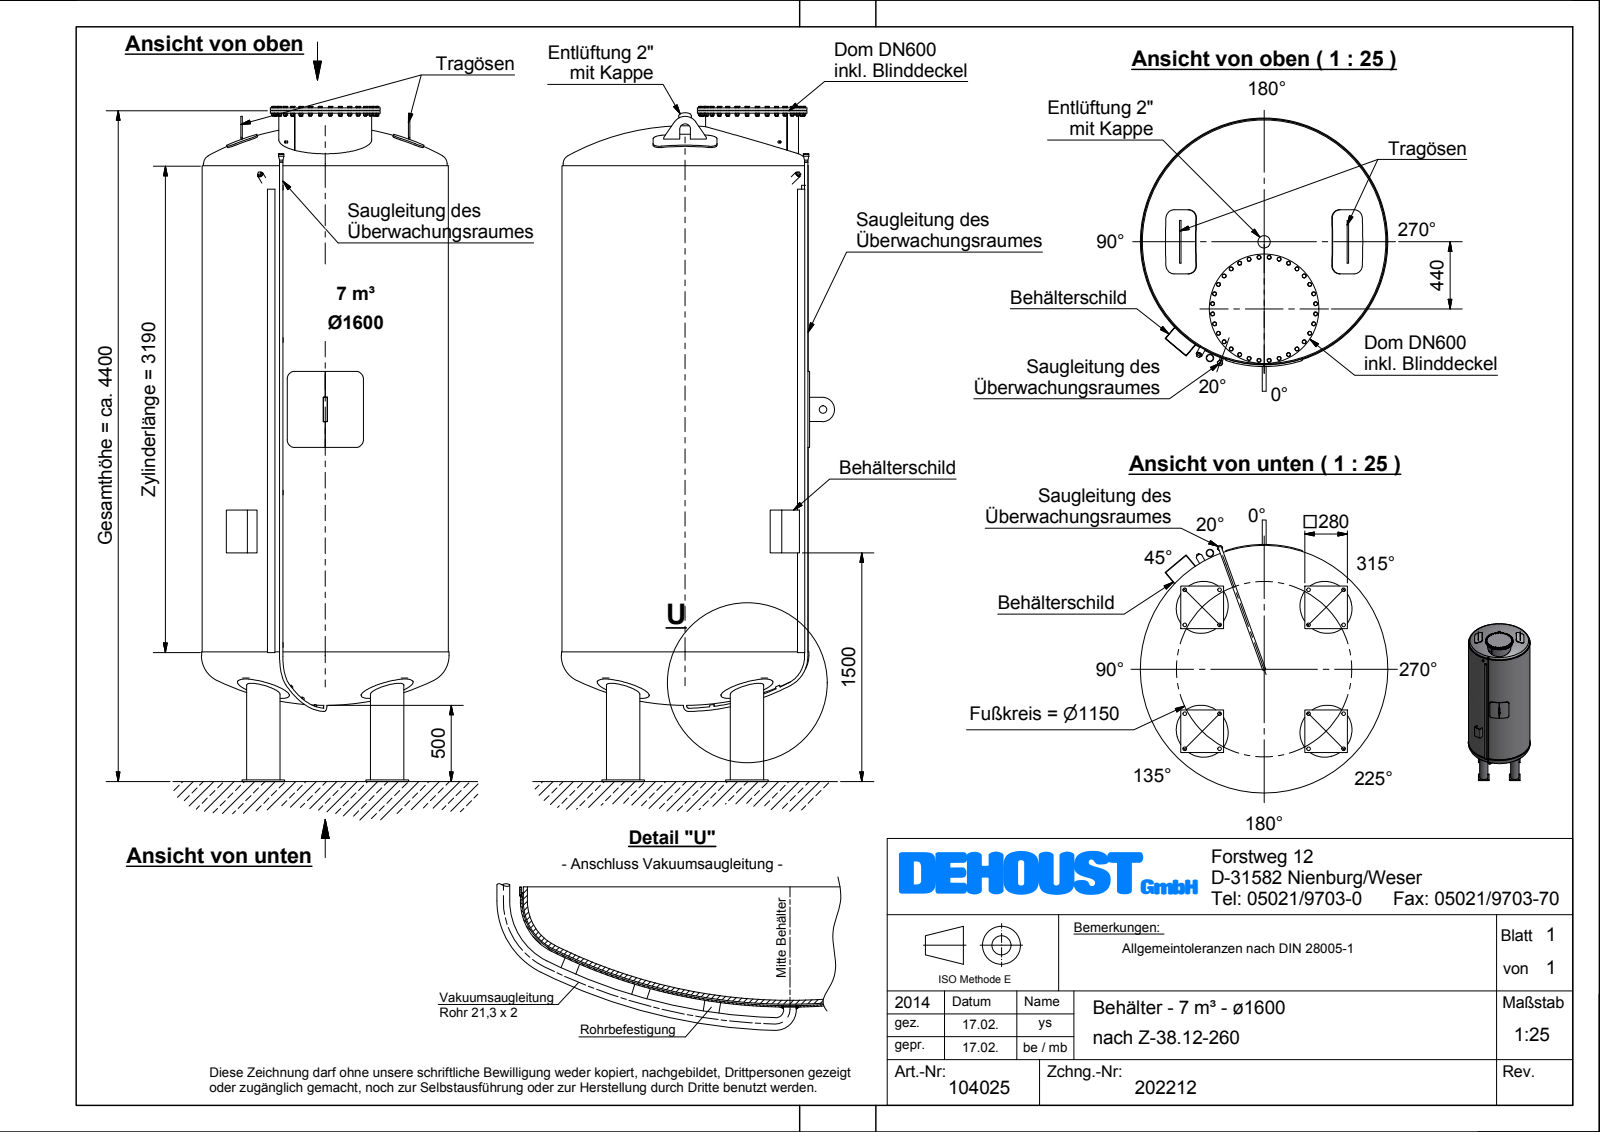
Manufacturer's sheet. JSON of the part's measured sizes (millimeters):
{"part_name": "Z-38_12-260_Beh\\S\\dlter_\\S\\x1600_007m\\S\\3_Dichte=1,0", "step_written_by": "Autodesk Inventor 2012 (AUTOMOTIVE_DESIGN)", "units": "millimeters", "bodies": {"solids": 8, "faces": 1156, "planar": 682, "cylindrical": 150, "other": 324}, "overall_size": [4429.34, 1720.38, 1624], "volume_mm3": 7094000000, "surface_area_mm2": 32340000, "round_holes": [[209.1, 4], [598, 1], [1590, 1]], "round_bosses_or_shafts": [[22.5, 32], [16, 32], [350, 4], [219.1, 4], [21.3, 2], [1624, 1], [1616, 1], [1600, 1]], "partial_cylinders_radius": [[56, 8], [50, 4], [35, 2], [85, 2], [80, 1], [818, 1]], "face_to_face_distances": [379.09, 344.09, 35, 4419.34, 10, 4040.25, 4384.34, 4030.25, 4374.34, 4409.34], "hole_center_spacings": [575, 813.17, 407.96, 939.16, 1150, 440]}
